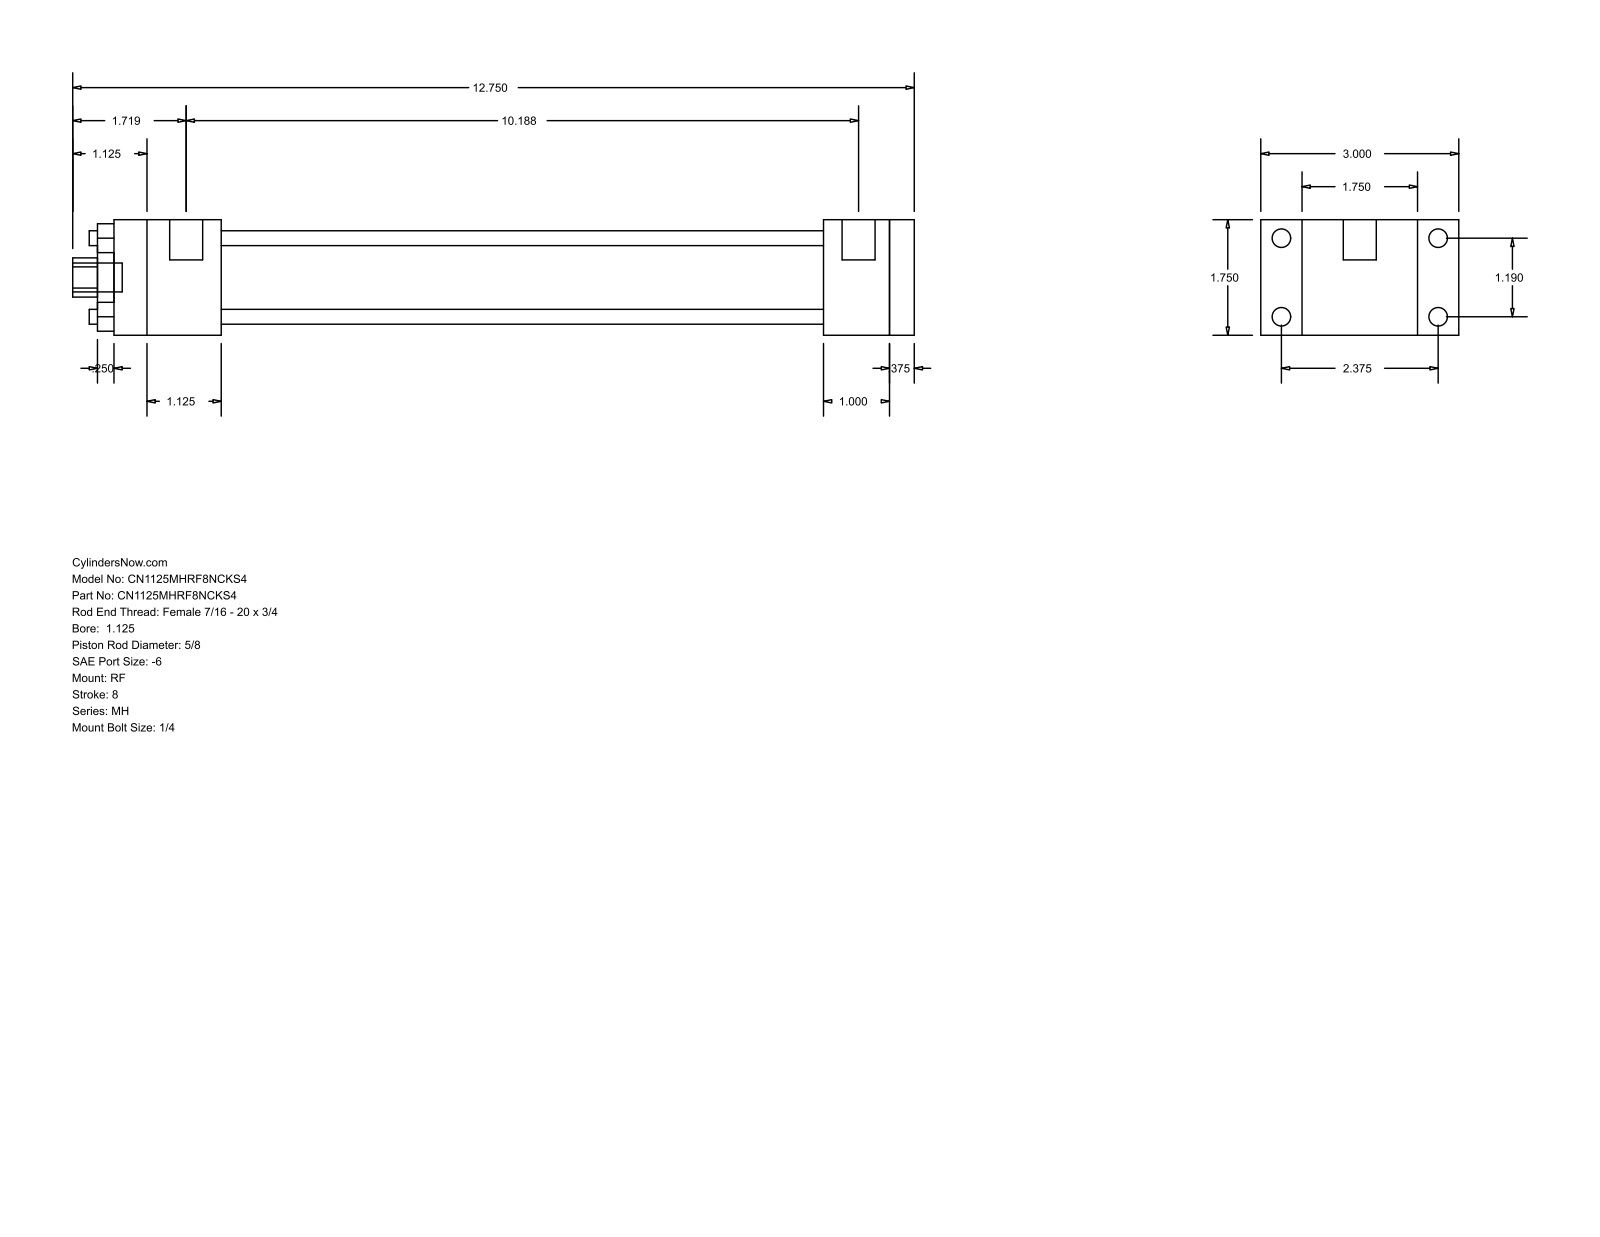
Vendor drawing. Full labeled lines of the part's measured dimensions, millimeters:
Part name (STEP PRODUCT): MH_RF__0112_0.625
STEP written by: GSSL Pune (CONFIG_CONTROL_DESIGN)
Units: millimetres
Bodies: 0 solids, 92 faces (64 planar, 28 cylindrical, 0 other)
Overall size (bounding box): 323.85 × 76.2 × 44.45
Round holes (diameter × count): ⌀5.71 ×4, ⌀15.88 ×1, ⌀28.57 ×1, ⌀34.92 ×1
Round bosses / shafts (diameter × count): ⌀7.14 ×4, ⌀5.56 ×4, ⌀12.7 ×2, ⌀11.11 ×1
Partial cylindrical surfaces — rounded edges, fillets, slot ends (radius × count): R7.54 ×1
Main face-to-face distances: 44.46, 9.53, 307.97, 15.87, 257.17, 266.7, 231.78, 25.39, 34.92, 41.27
Hole centre spacings: 21.37, 30.22, 42.74
